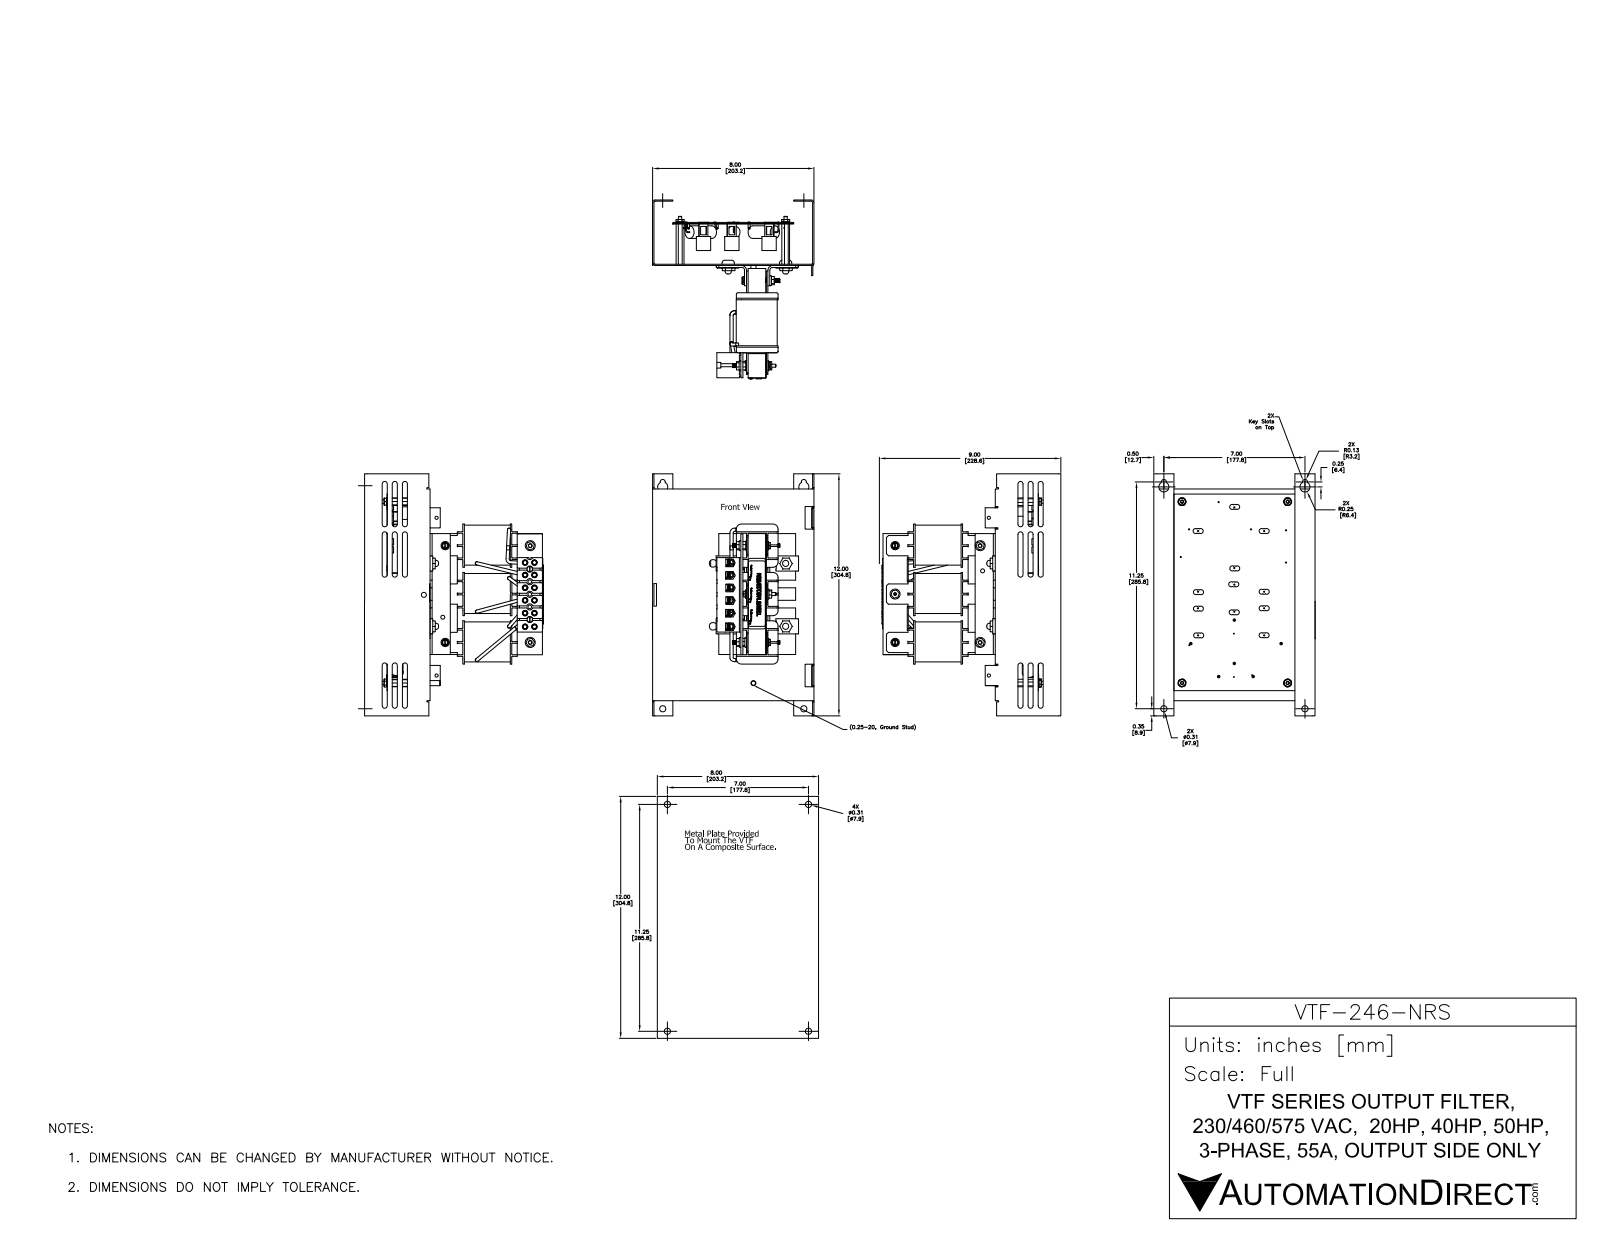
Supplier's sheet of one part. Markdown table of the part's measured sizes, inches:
| quantity | value |
| --- | --- |
| part name | VTF 35-55 Coordfix from XT VTF 80A r1ext comb 1 |
| STEP written by | SolidWorks 2017 (AUTOMOTIVE_DESIGN) |
| units | inches |
| bodies | 63 solids, 5091 faces (2967 planar, 1547 cylindrical, 577 other) |
| overall size | 12 × 9.143 × 8.005 |
| volume | 105.5 in³ |
| surface area | 1 379 in² |
| round holes (diameter × count) | 0.06 × 24, 0.251 × 12, 0.25 × 6, 0.38 × 6, 0.156 × 5, 0.193 × 5, 0.124 × 4, 0.149 × 4, 0.19 × 4, 0.22 × 4, 0.31 × 4, 0.11 × 3 |
| round bosses / shafts (diameter × count) | 0.2 × 26, 0.03 × 12, 0.046 × 11, 0.125 × 6, 0.5 × 5, 0.37 × 5, 0.241 × 5, 0.608 × 4 |
| partial cylindrical surfaces (radius × count) | 0.025 × 116, 0.125 × 92, 0.012 × 37, 0.062 × 26, 0.077 × 24, 0.25 × 24, 0.013 × 17, 0.063 × 16 |
| main face-to-face distances | 0.063, 2.074, 2.01, 0.075, 7.937, 2.063, 2, 2.136, 2.073, 0.073 |
| hole center spacings | 0.794, 0.58, 0.543, 0.911, 0.954, 0.993, 1.16, 1.16 |
